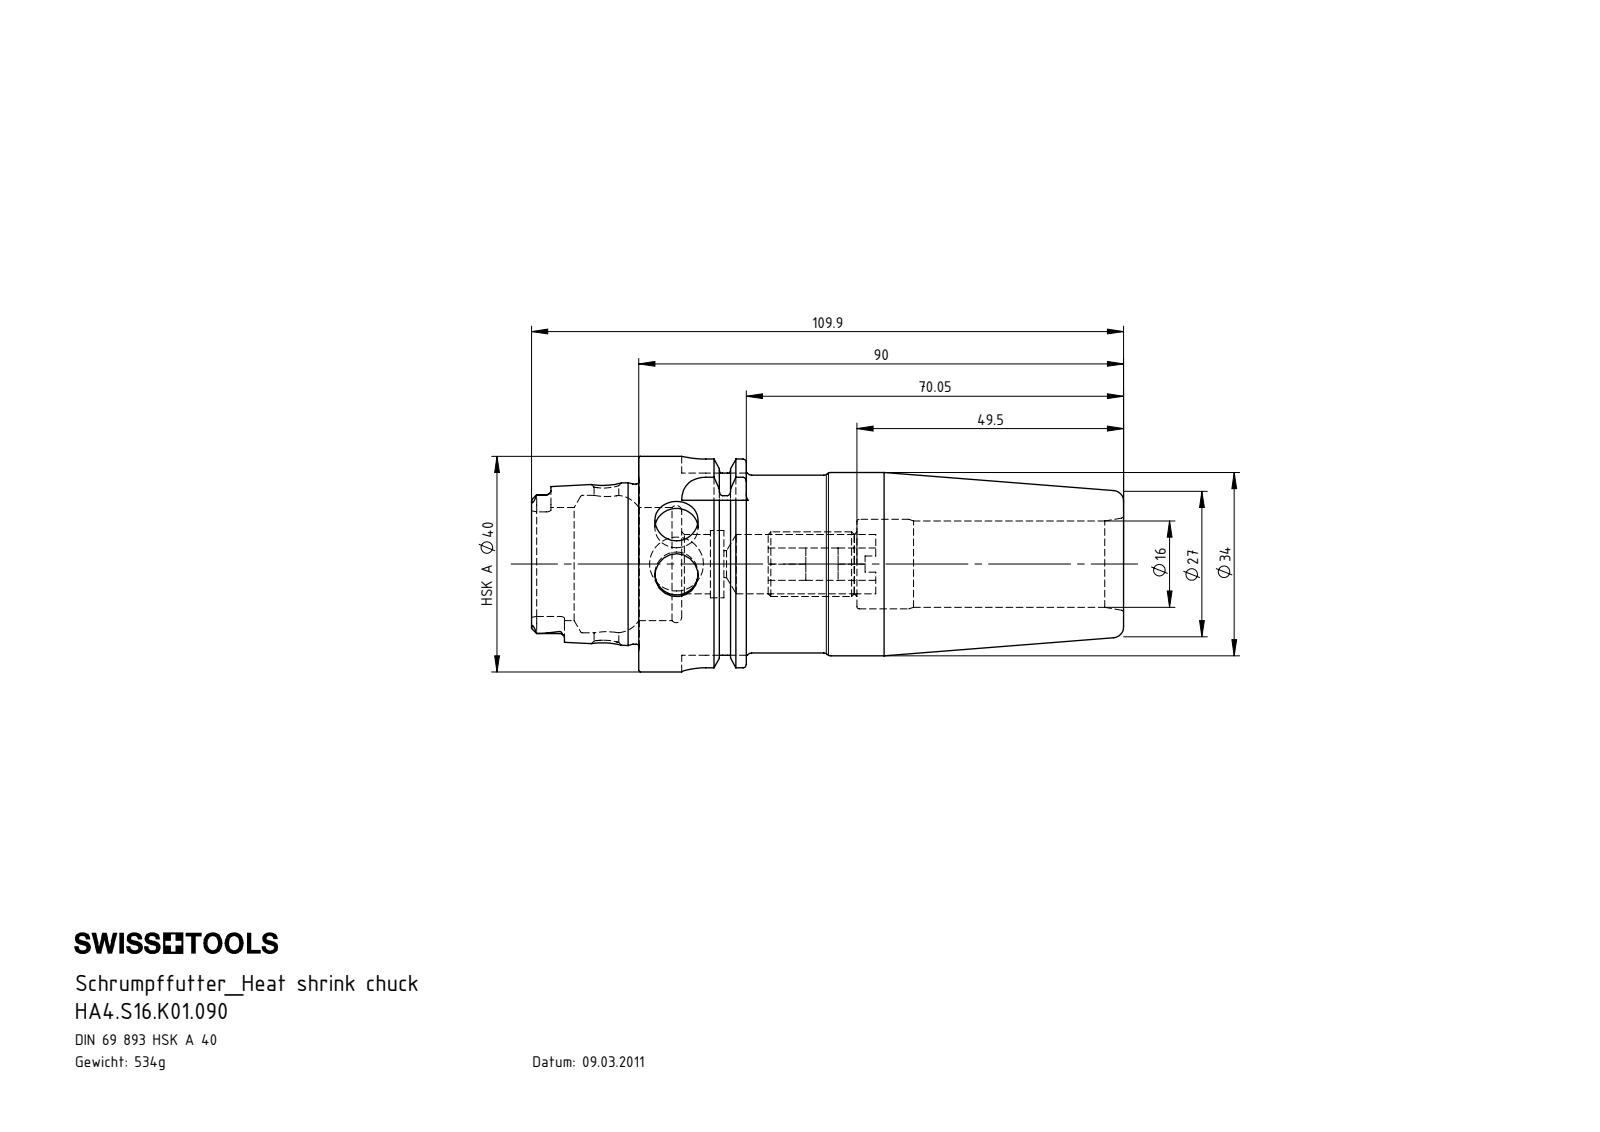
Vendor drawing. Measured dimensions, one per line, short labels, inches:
name: HA4-S16.K01.090; ERU-AN5.K01.020_A; HA4-S16.K01.090_C_Fertigbearbeitung
written by: SolidWorks 2012 (AUTOMOTIVE_DESIGN)
unit: in
bodies: 2 solids, 233 faces (82 planar, 64 cylindrical, 87 other)
size: 4.327 × 1.575 × 1.575
volume: 4.148 in³; area: 32.24 in²
holes: 2× ⌀0.315, 1× ⌀0.181, 1× ⌀0.197, 1× ⌀0.236, 1× ⌀0.394, 1× ⌀0.433, 1× ⌀0.492, 1× ⌀0.63, 1× ⌀0.654, 1× ⌀0.827, 1× ⌀1.004
bosses: 1× ⌀1.575, 1× ⌀1.368, 1× ⌀1.339, 1× ⌀1.299, 1× ⌀1.17, 1× ⌀0.472
rounds: 6× R0.035, 4× R0.074, 4× R0.177
face distances: 0.783, 0.313, 0.785, 0.472, 3.543, 3.23, 2.758, 0.236, 1.096, 1.569
